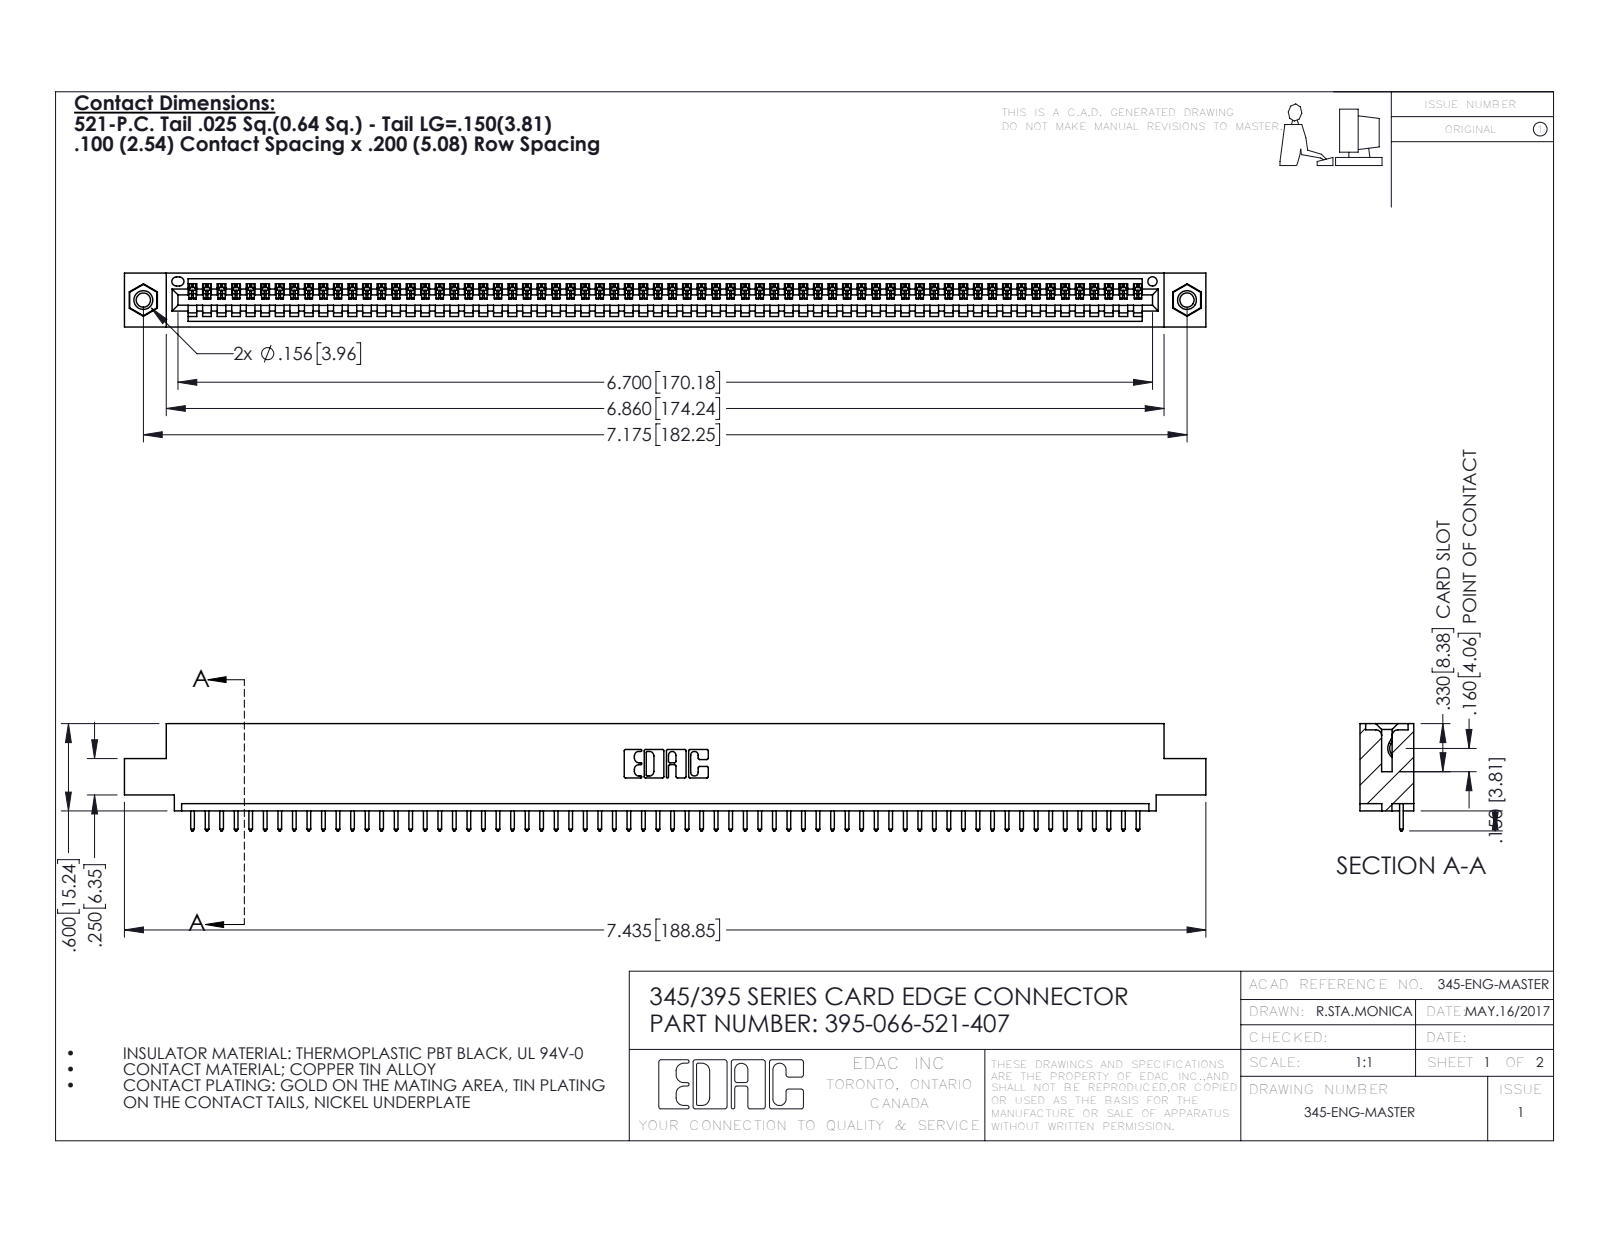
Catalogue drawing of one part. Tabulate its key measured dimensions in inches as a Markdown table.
| quantity | value |
| --- | --- |
| part name | 345-250-001_345-250-005-103; 395-066-521-407; 345-292-001_345-293-121; 345 Part_0.110 Offset - 0.156 Dia-TI |
| STEP written by | SolidWorks 2016 (CONFIG_CONTROL_DESIGN) |
| units | inches |
| bodies | 69 solids, 4018 faces (2756 planar, 1246 cylindrical, 16 other) |
| overall size | 7.435 × 0.737 × 0.37 |
| volume | 1.09 in³ |
| surface area | 36.33 in² |
| round holes (diameter × count) | 0.098 × 2, 0.125 × 2, 0.156 × 2, 0.064 × 1 |
| round bosses / shafts (diameter × count) | 0.155 × 2 |
| partial cylindrical surfaces (radius × count) | 0.006 × 132, 0.01 × 132, 0.01 × 22, 0.007 × 6, 0.031 × 6, 0.026 × 3, 0.031 × 2, 0.04 × 2 |
| main face-to-face distances | 0.072, 0.298, 0.37, 0.2, 0.098, 0.272, 0.025, 0.225, 0.149, 0.072 |
| hole center spacings | 0.27, 6.939, 7.175 |
